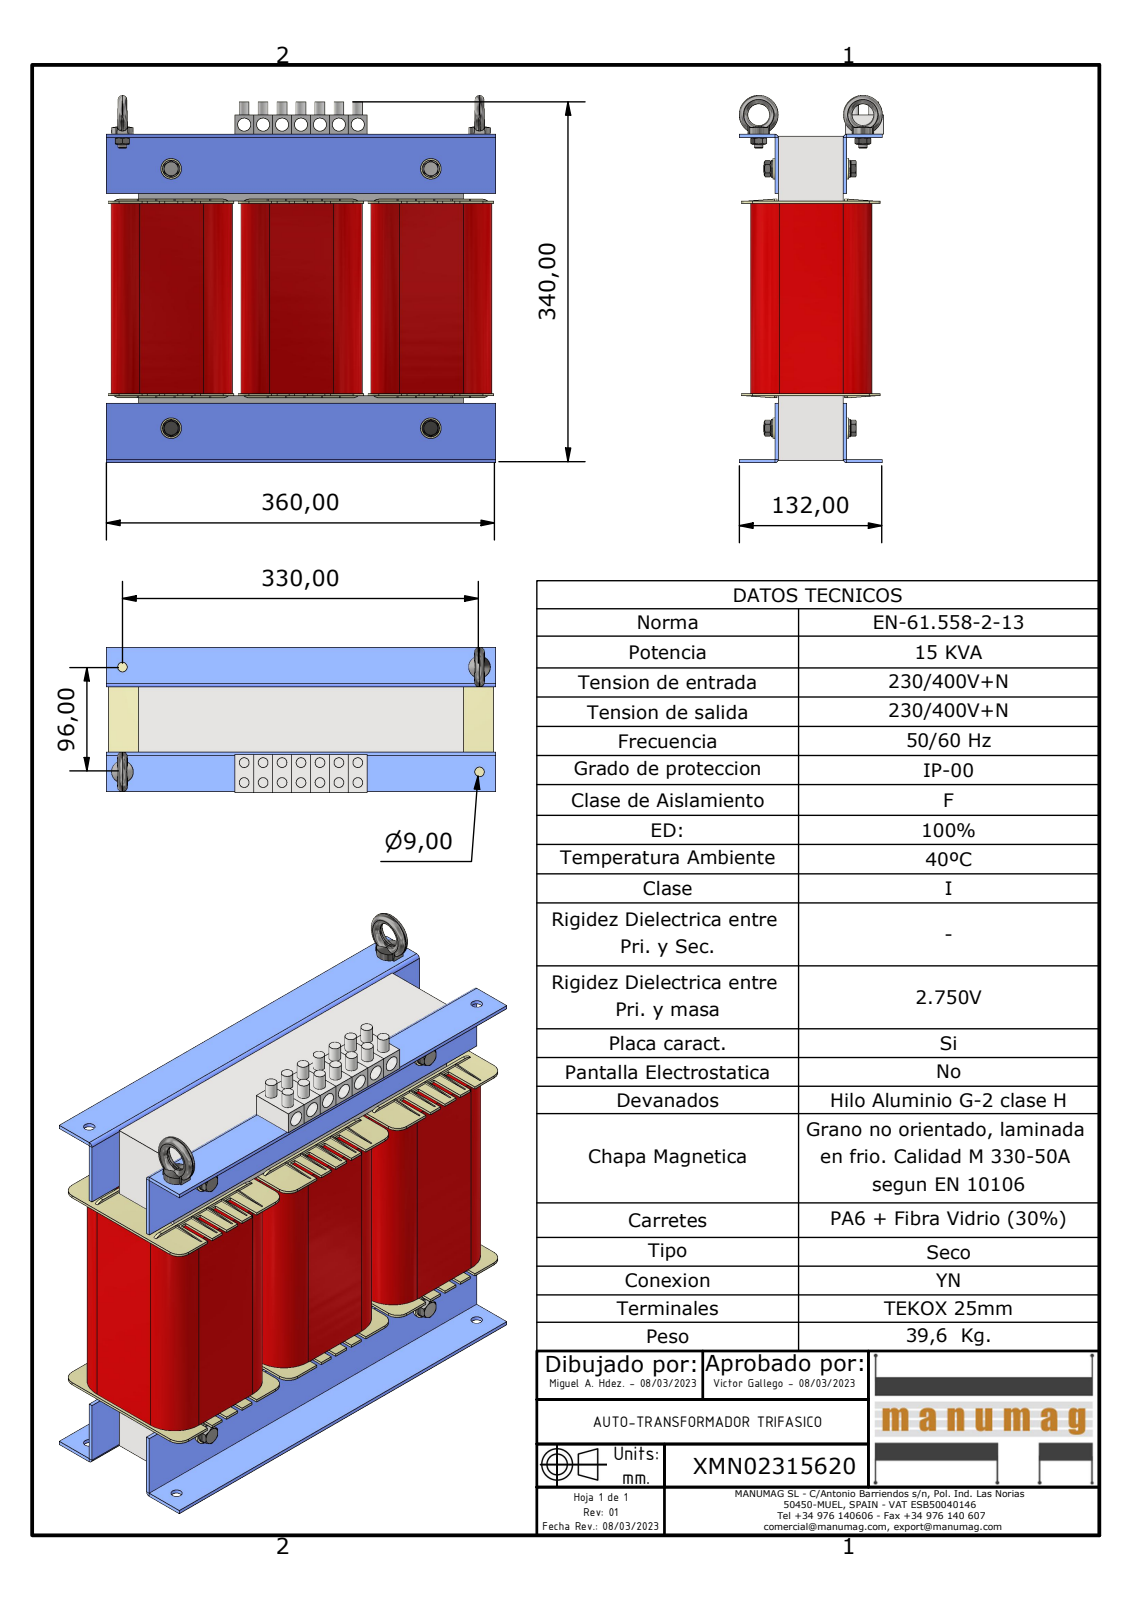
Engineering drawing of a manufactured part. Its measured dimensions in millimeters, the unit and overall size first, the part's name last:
Units: millimetres
Overall size (bounding box): 360 × 340 × 133
Round holes (diameter × count): ⌀12 ×7, ⌀6.65 ×6, ⌀8 ×4, ⌀8.4 ×4, ⌀9 ×4, ⌀10.5 ×4, ⌀11 ×4, ⌀20 ×2
Round bosses / shafts (diameter × count): ⌀9 ×14, ⌀19 ×4, ⌀16 ×4, ⌀11.4 ×4, ⌀9.6 ×4, ⌀7.32 ×4, ⌀36 ×2, ⌀8 ×2
Partial cylindrical surfaces — rounded edges, fillets, slot ends (radius × count): R10 ×26, R1 ×23, R2 ×15, R2.35 ×12, R26.53 ×12, R9 ×6, R3 ×4, R4 ×4
Main face-to-face distances: 1, 60, 2, 62, 240, 61, 63, 3, 24.53, 25.53
Hole centre spacings: 17.5, 35, 52.5, 240, 70, 96, 78.91, 87.5
Volume: 8 989 000 mm³ · Surface area: 1 313 000 mm²
Bodies: 43 solids, 1303 faces (949 planar, 262 cylindrical, 92 other)
Part name (STEP PRODUCT): XMN02315620; UI 180 - 60 (300x300); UI 180_60_BOBINADO; RC60 NT060 (+7 more)
STEP written by: Autodesk Inventor 2023 (AUTOMOTIVE_DESIGN)
